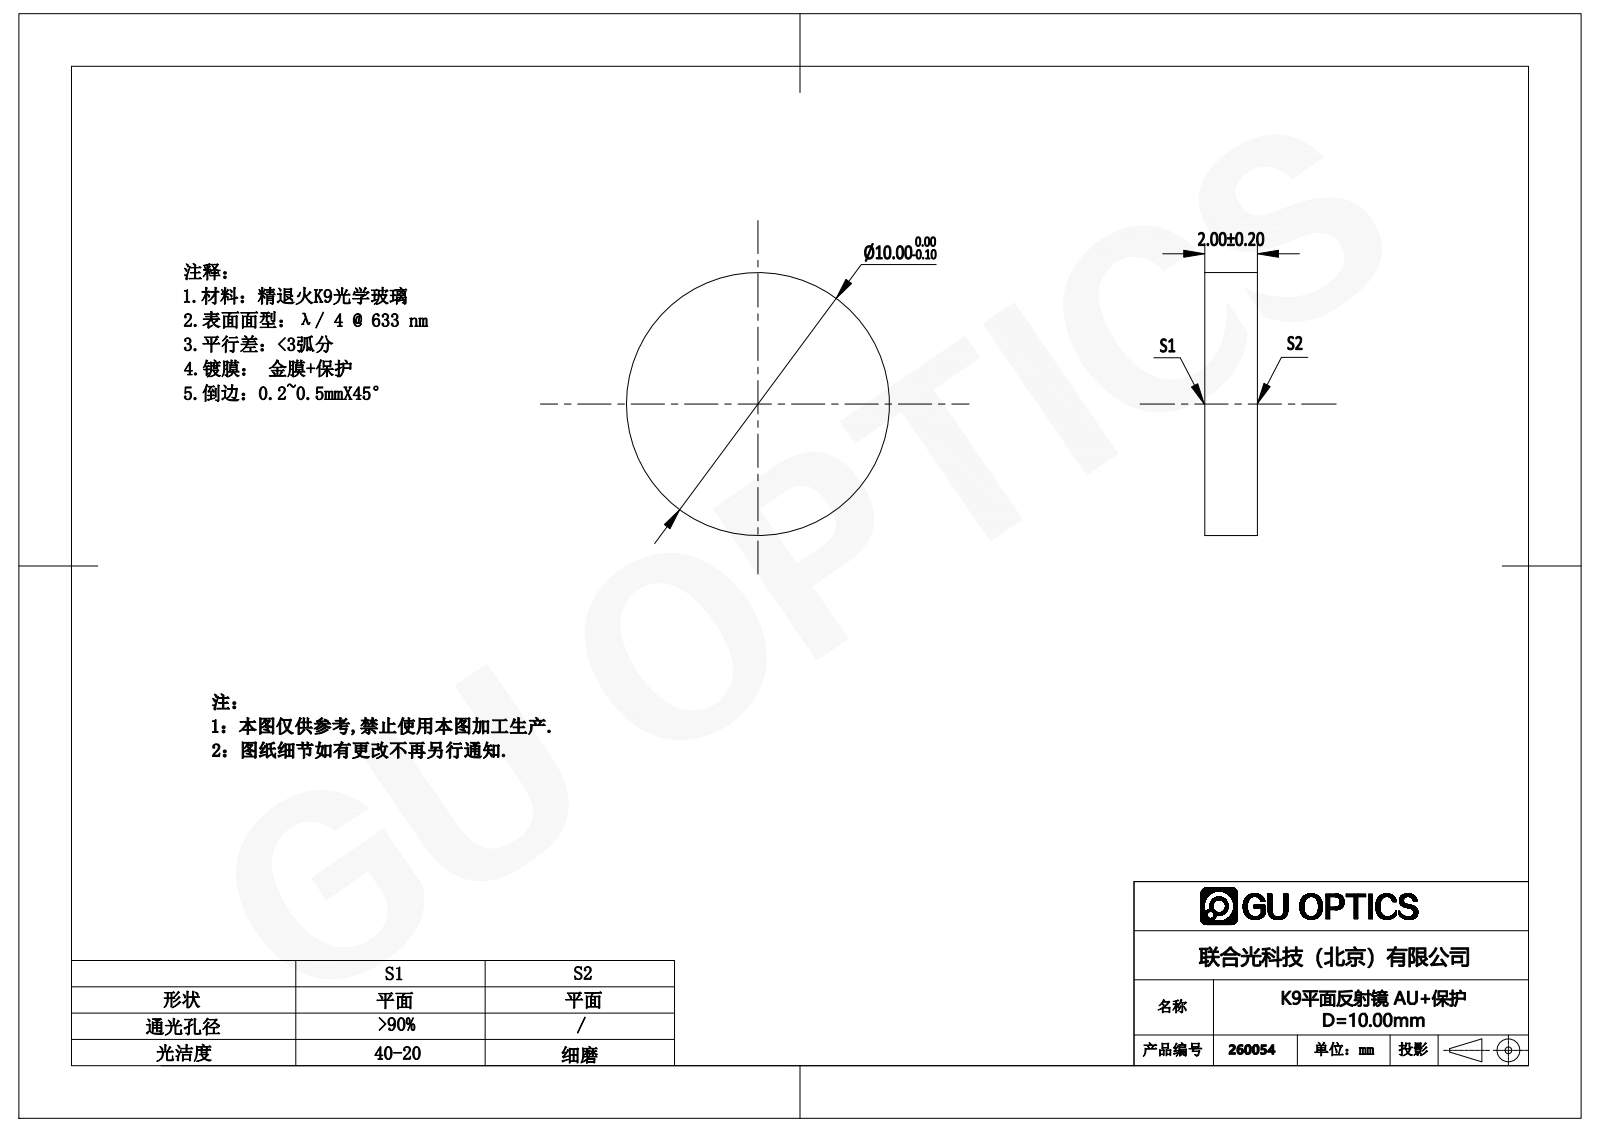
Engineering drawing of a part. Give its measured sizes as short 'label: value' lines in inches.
name: 260002
written by: SolidWorks 2016 (AUTOMOTIVE_DESIGN)
unit: in
bodies: 1 solid, 4 faces (2 planar, 2 cylindrical, 0 other)
size: 0.394 × 0.394 × 0.079
volume: 0.01 in³; area: 0.341 in²
bosses: 1× ⌀0.394
face distances: 0.079
